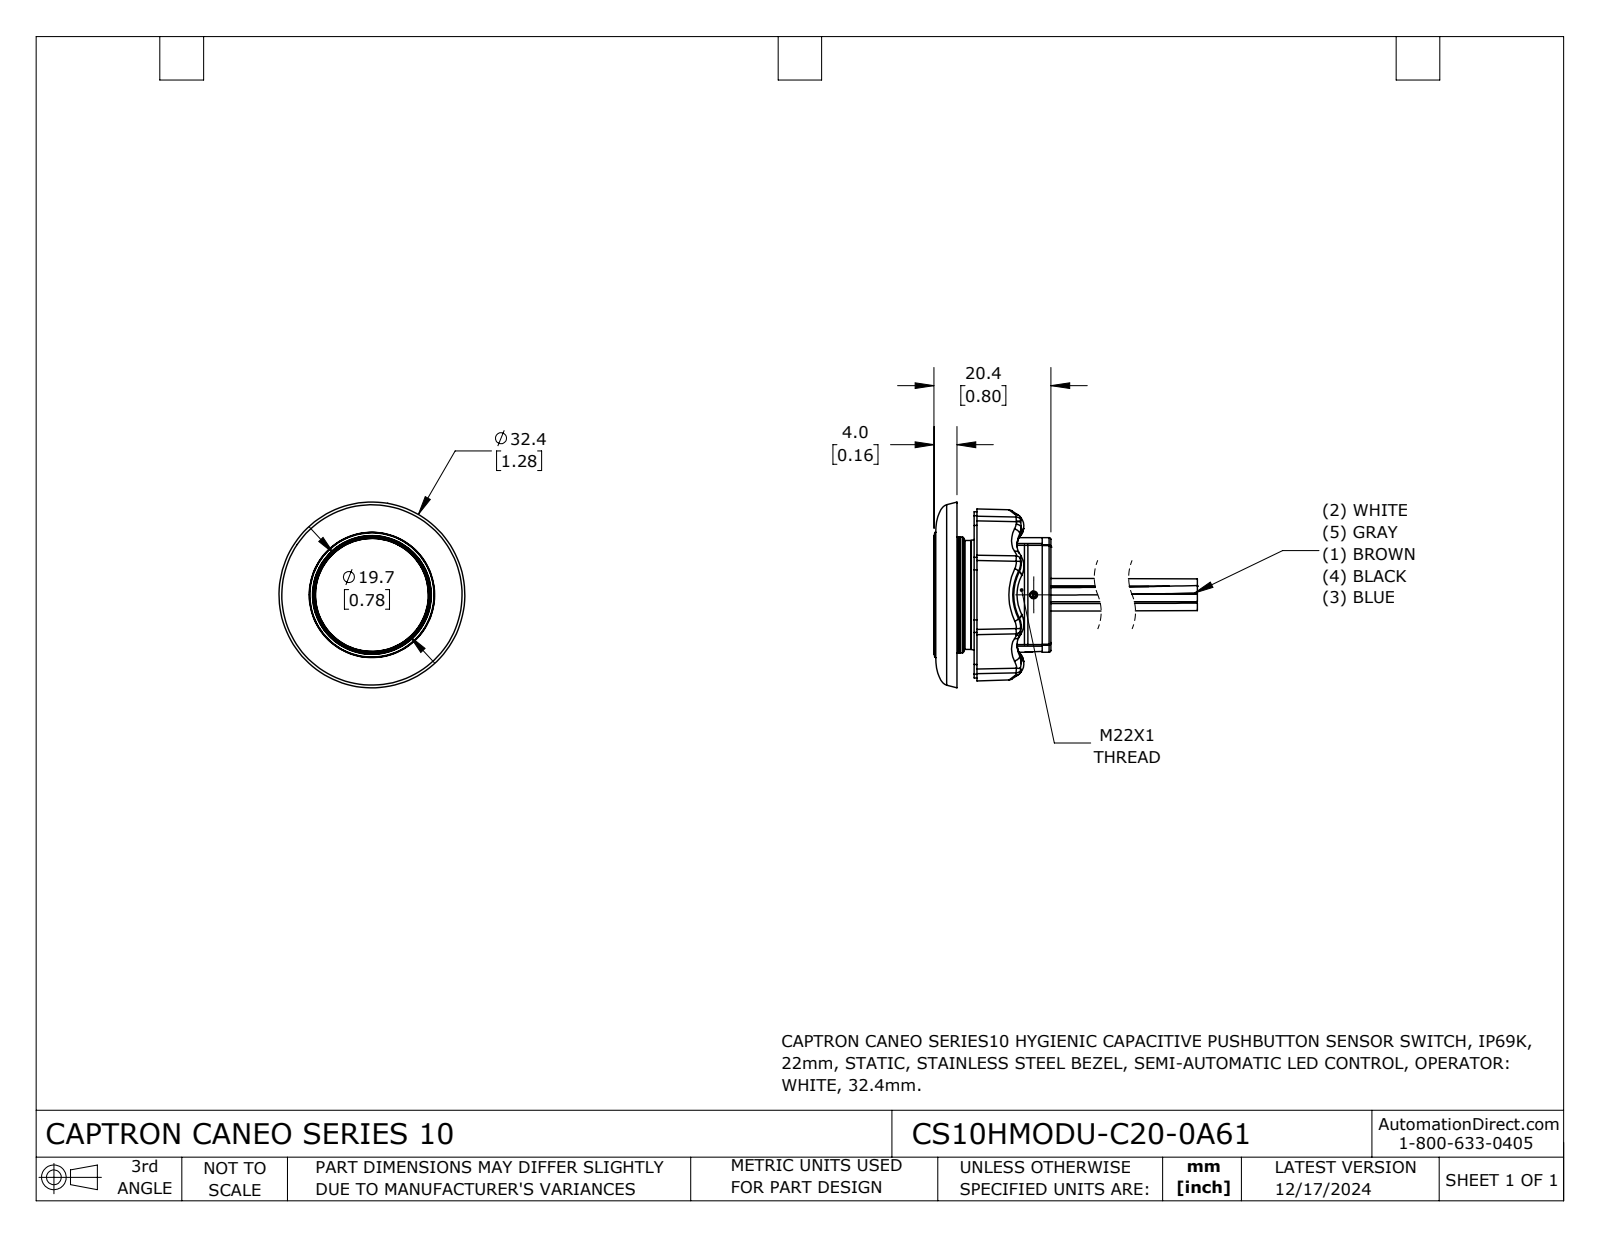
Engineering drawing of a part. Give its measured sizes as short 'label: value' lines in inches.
name: CS10HMODU-C20-0A61
written by: SolidWorks 2024 (CONFIG_CONTROL_DESIGN)
unit: in
bodies: 7 solids, 854 faces (403 planar, 138 cylindrical, 313 other)
size: 1.803 × 1.277 × 1.277
volume: 0.636 in³; area: 9.99 in²
holes: 1× ⌀0.053, 1× ⌀0.827, 1× ⌀0.927, 1× ⌀1.004
bosses: 1× ⌀0.748, 1× ⌀0.724
rounds: 20× R0.006, 6× R0.004, 6× R0.118, 6× R0.295, 4× R0.012, 4× R0.039, 4× R0.689, 1× R0.196
face distances: 0.157, 0.646, 0.803, 0.134, 0.016, 0.528, 0.142, 0.118, 0.276, 0.661
